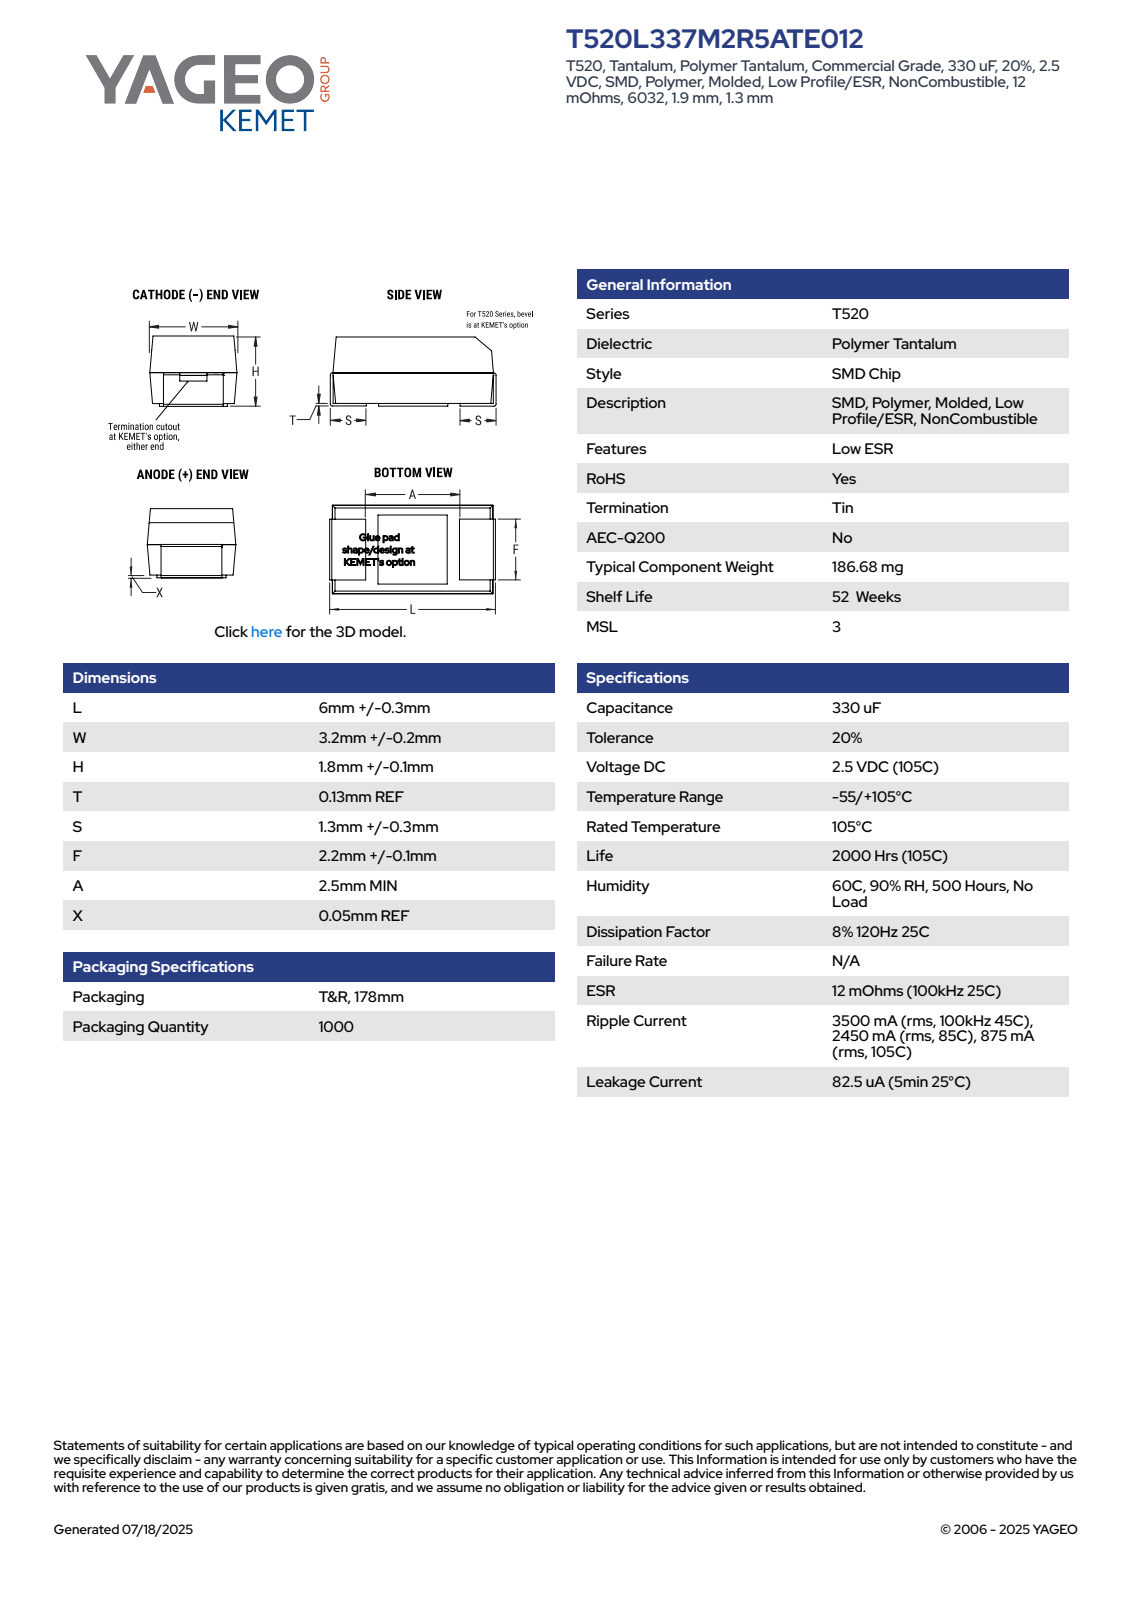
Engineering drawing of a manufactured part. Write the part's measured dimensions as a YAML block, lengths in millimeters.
part_name: "CTS_TCM2NOBNOKBOPT_6032_L6.3W3.4H1.9T0.13S1.3F2.3A2.5X0.05"
step_written_by: "SolidWorks 2014 (AUTOMOTIVE_DESIGN)"
units: millimeters
bodies: {solids: 4, faces: 90, planar: 86, cylindrical: 4, other: 0}
overall_size: [6.3, 3.4, 1.91]
volume: 36
surface_area: 84
partial_cylinders:
  - {radius: 0.13, count: 4}
face_to_face_distances: [1.82, 5.93, 1.77, 1.9, 3.37, 3.38, 6.17, 6.04, 6.3, 1.3]
